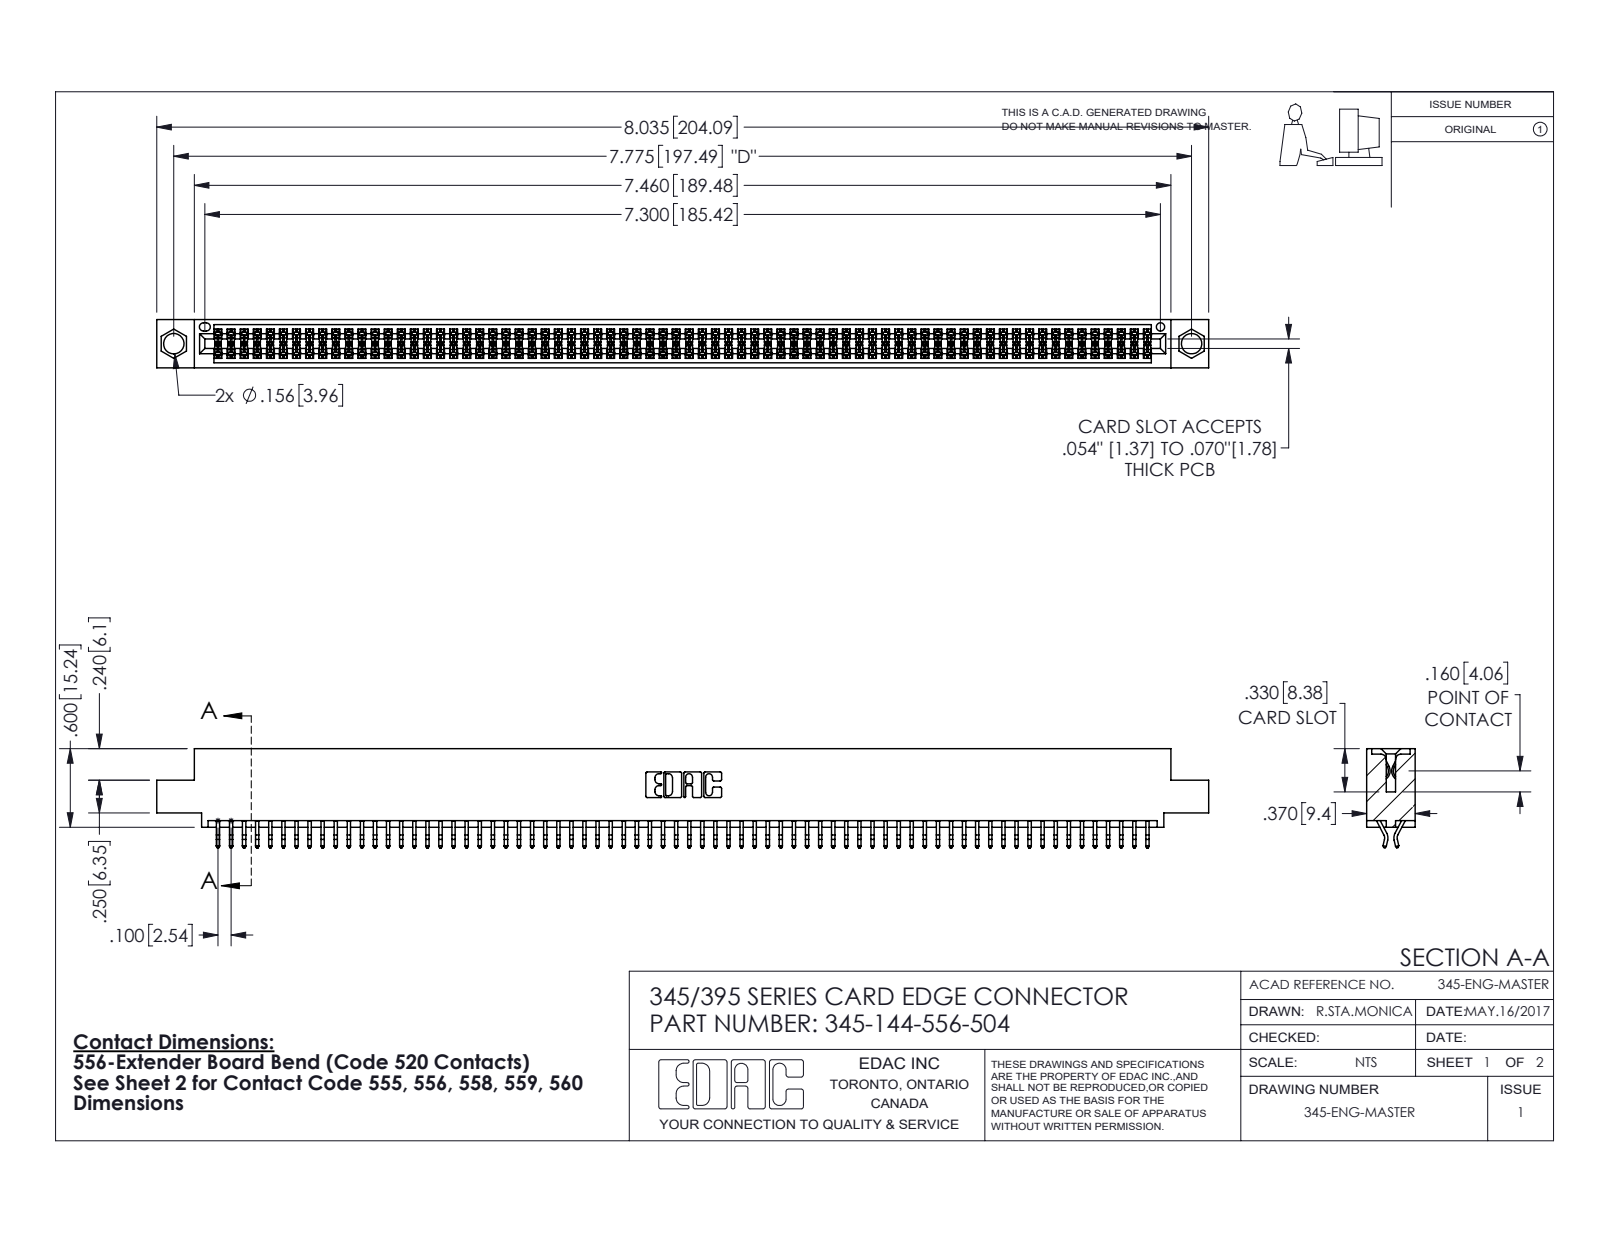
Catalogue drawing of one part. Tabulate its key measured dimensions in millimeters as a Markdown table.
| quantity | value |
| --- | --- |
| part name | 345-292-001_556 Tail; 345 Part_0.110 Offset - 0.156 Dia-TI; 345-144-556-504 |
| STEP written by | SolidWorks 2020 (CONFIG_CONTROL_DESIGN) |
| units | millimeters |
| bodies | 145 solids, 8208 faces (5426 planar, 2782 cylindrical, 0 other) |
| overall size | 204.1 × 19.2 × 9.4 |
| volume | 19 930 mm³ |
| surface area | 29 850 mm² |
| round holes (diameter × count) | 4 × 2, 1.6 × 1 |
| partial cylindrical surfaces (radius × count) | 0.2 × 288, 0.3 × 22, 0.2 × 6, 0.8 × 6, 0.7 × 3, 0.3 × 2, 0.4 × 2, 0.5 × 2 |
| main face-to-face distances | 7.6, 1.8, 9.4, 5.1, 0.6, 2.5, 6.9, 5.7, 4.4, 3.8 |
| hole center spacings | 6.9, 191.5, 197.5 |
